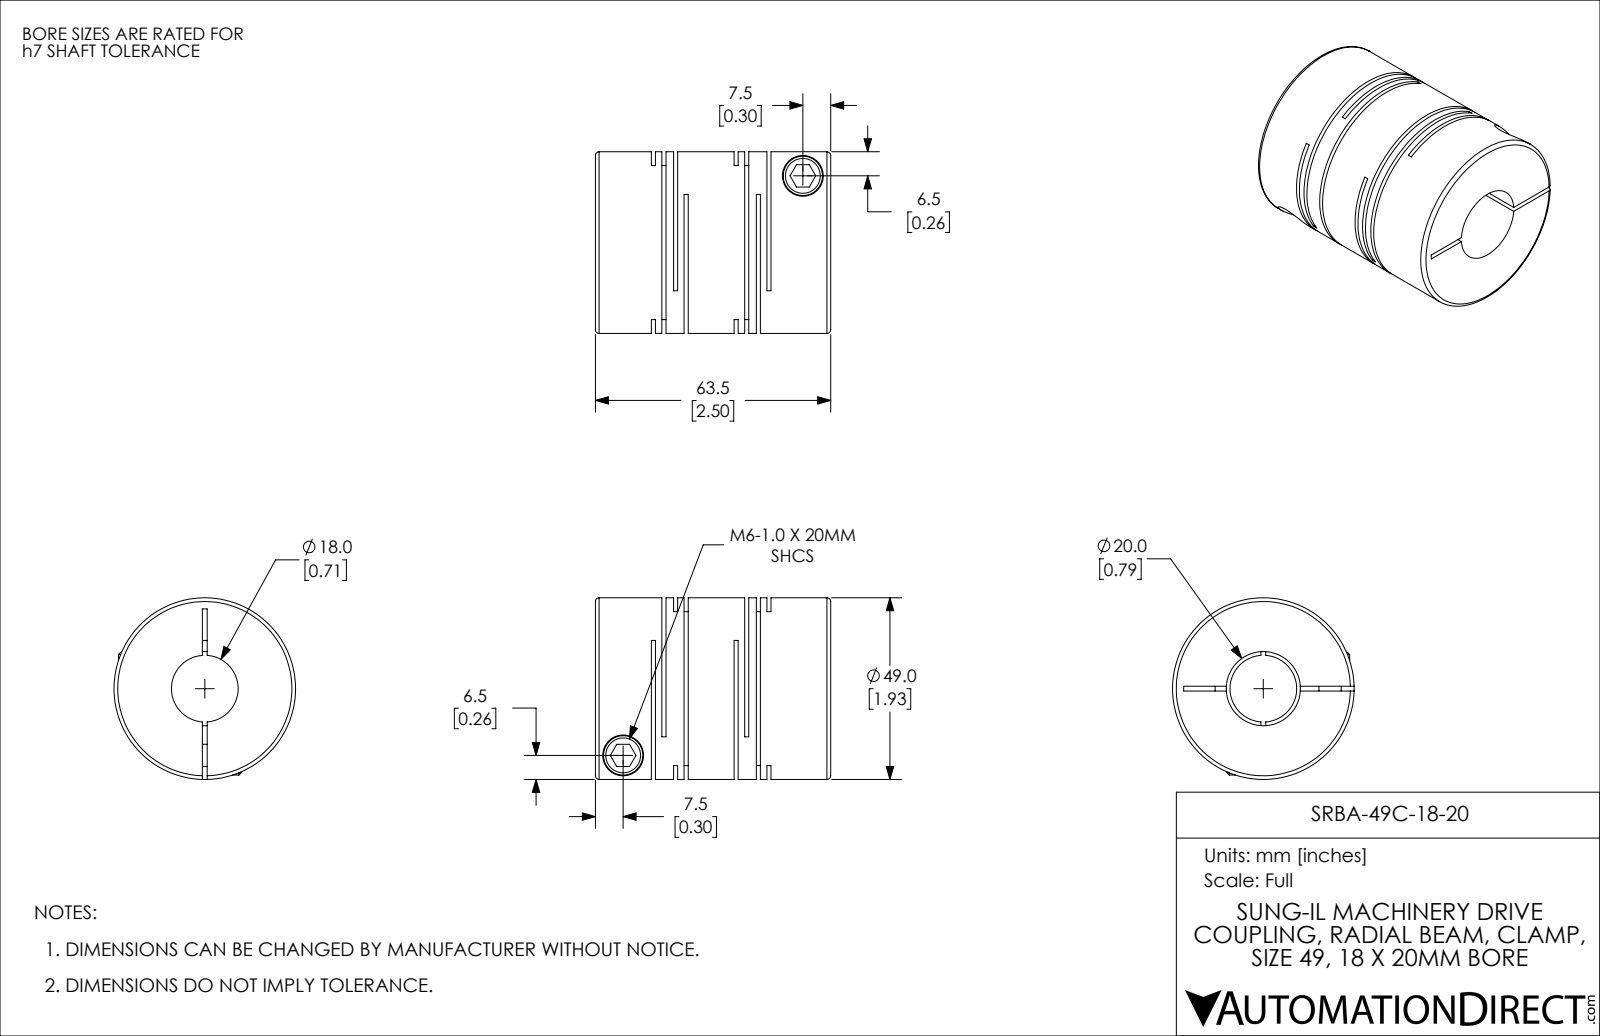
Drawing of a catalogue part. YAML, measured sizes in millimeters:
part_name: "SRBA-49C-18-20"
step_written_by: "SolidWorks 2021 (CONFIG_CONTROL_DESIGN)"
units: millimeters
bodies: {solids: 1, faces: 114, planar: 60, cylindrical: 42, other: 12}
overall_size: [63.5, 49, 49]
volume: 87092
surface_area: 38048
round_holes:
  - {diameter: 6, count: 2}
  - {diameter: 11, count: 2}
  - {diameter: 18, count: 1}
  - {diameter: 20, count: 1}
round_bosses_or_shafts:
  - {diameter: 10.6, count: 2}
  - {diameter: 49, count: 1}
face_to_face_distances: [6, 1.1, 2.85, 22.35, 1.75, 4.9, 21.25, 3.15, 19.5, 16.35]
